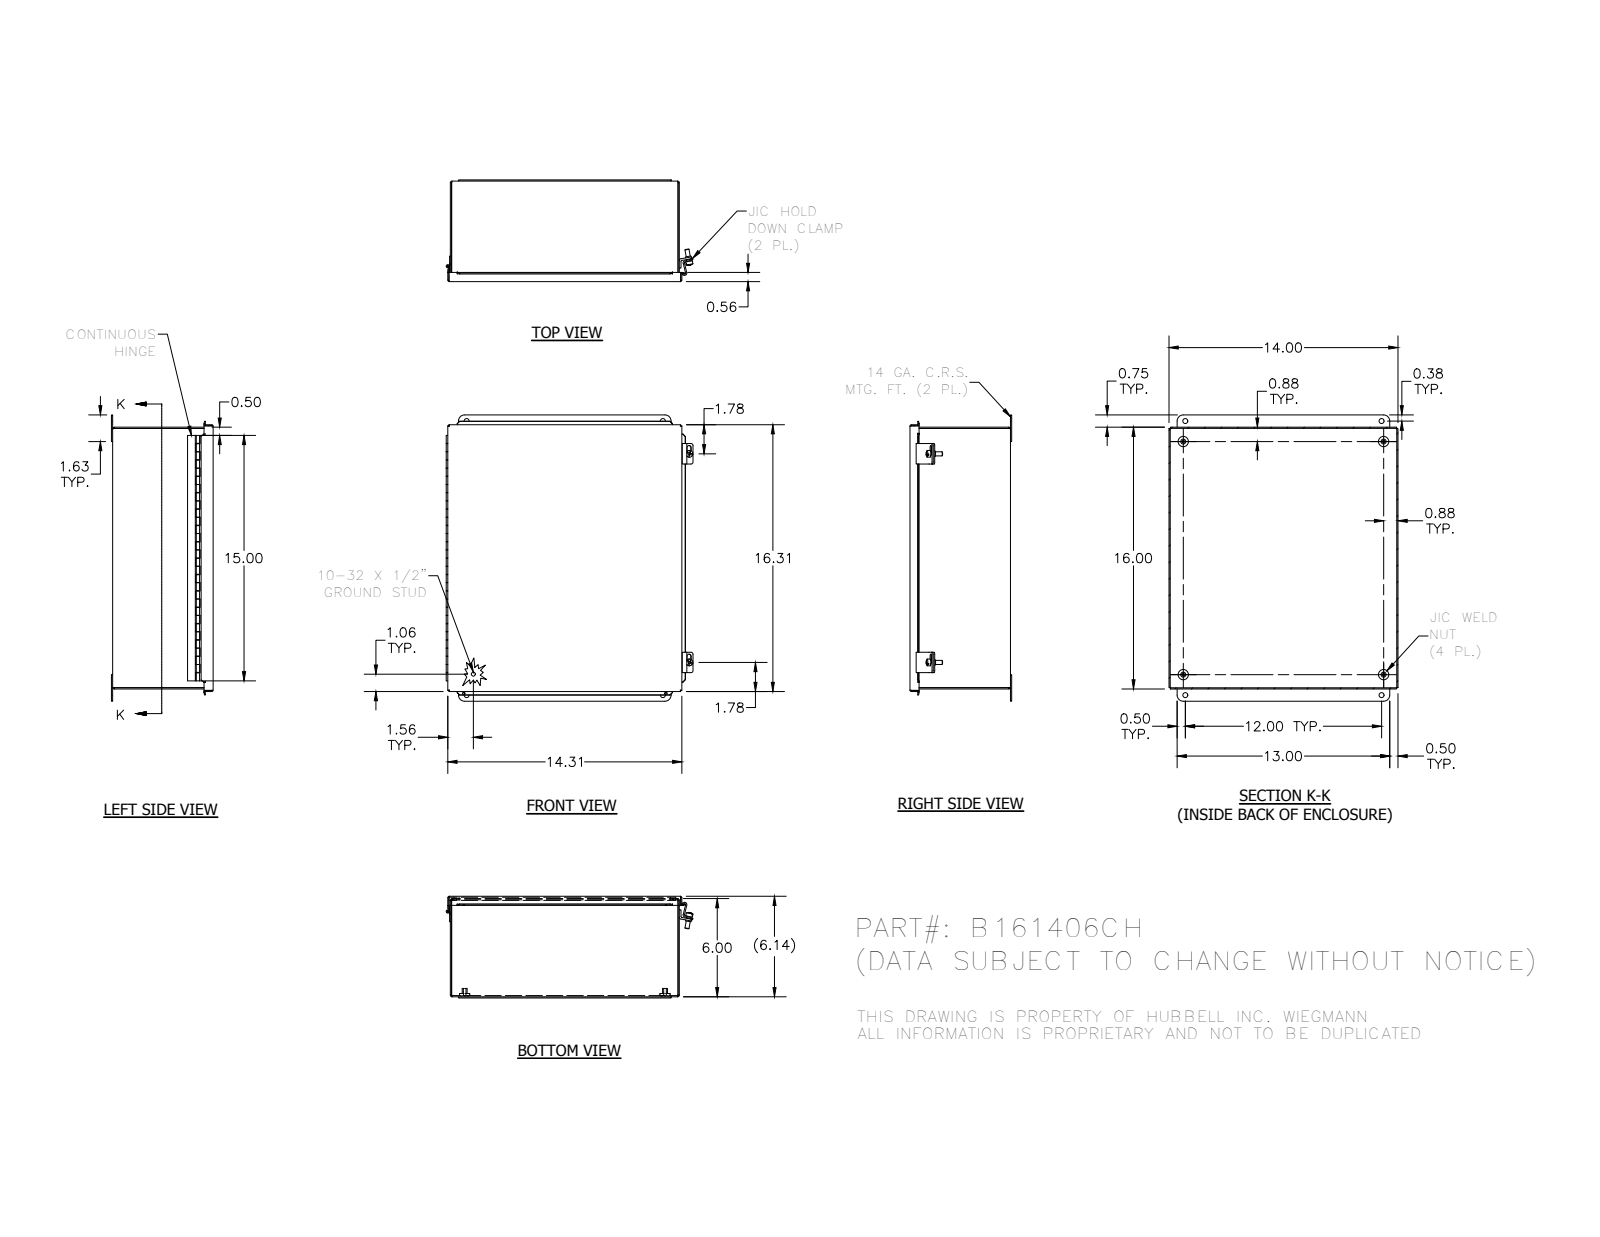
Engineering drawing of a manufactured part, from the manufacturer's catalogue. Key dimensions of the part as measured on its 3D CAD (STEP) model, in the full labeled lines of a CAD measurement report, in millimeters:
Part name (STEP PRODUCT): B161406CH; 3499; 3486; C1001 (+8 more)
STEP written by: Autodesk Inventor 2012 (AUTOMOTIVE_DESIGN)
Units: millimetres
Bodies: 20 solids, 539 faces (347 planar, 147 cylindrical, 45 other)
Overall size (bounding box): 444.5 × 383.2 × 158
Volume: 1 191 000 mm³ · Surface area: 1 294 000 mm²
Round holes (diameter × count): ⌀4 ×4, ⌀7.9 ×4, ⌀3.6 ×2, ⌀5 ×2, ⌀2.9 ×1
Round bosses / shafts (diameter × count): ⌀15.9 ×4, ⌀7.6 ×4, ⌀6.4 ×3, ⌀10.4 ×2, ⌀8.7 ×2, ⌀5.1 ×1, ⌀4.8 ×1, ⌀2.5 ×1
Partial cylindrical surfaces — rounded edges, fillets, slot ends (radius × count): R0.8 ×15, R2.7 ×8, R3.2 ×8, R2.4 ×7, R3.4 ×4, R9.5 ×4, R1.6 ×3, R3.2 ×3
Main face-to-face distances: 1.9, 154.5, 1.6, 156.1, 152.6, 154.2, 353.7, 404.5, 355.6, 351.8
Hole centre spacings: 31.9, 309.6, 393.7, 499.9, 304.8, 311.2, 362, 425.5
